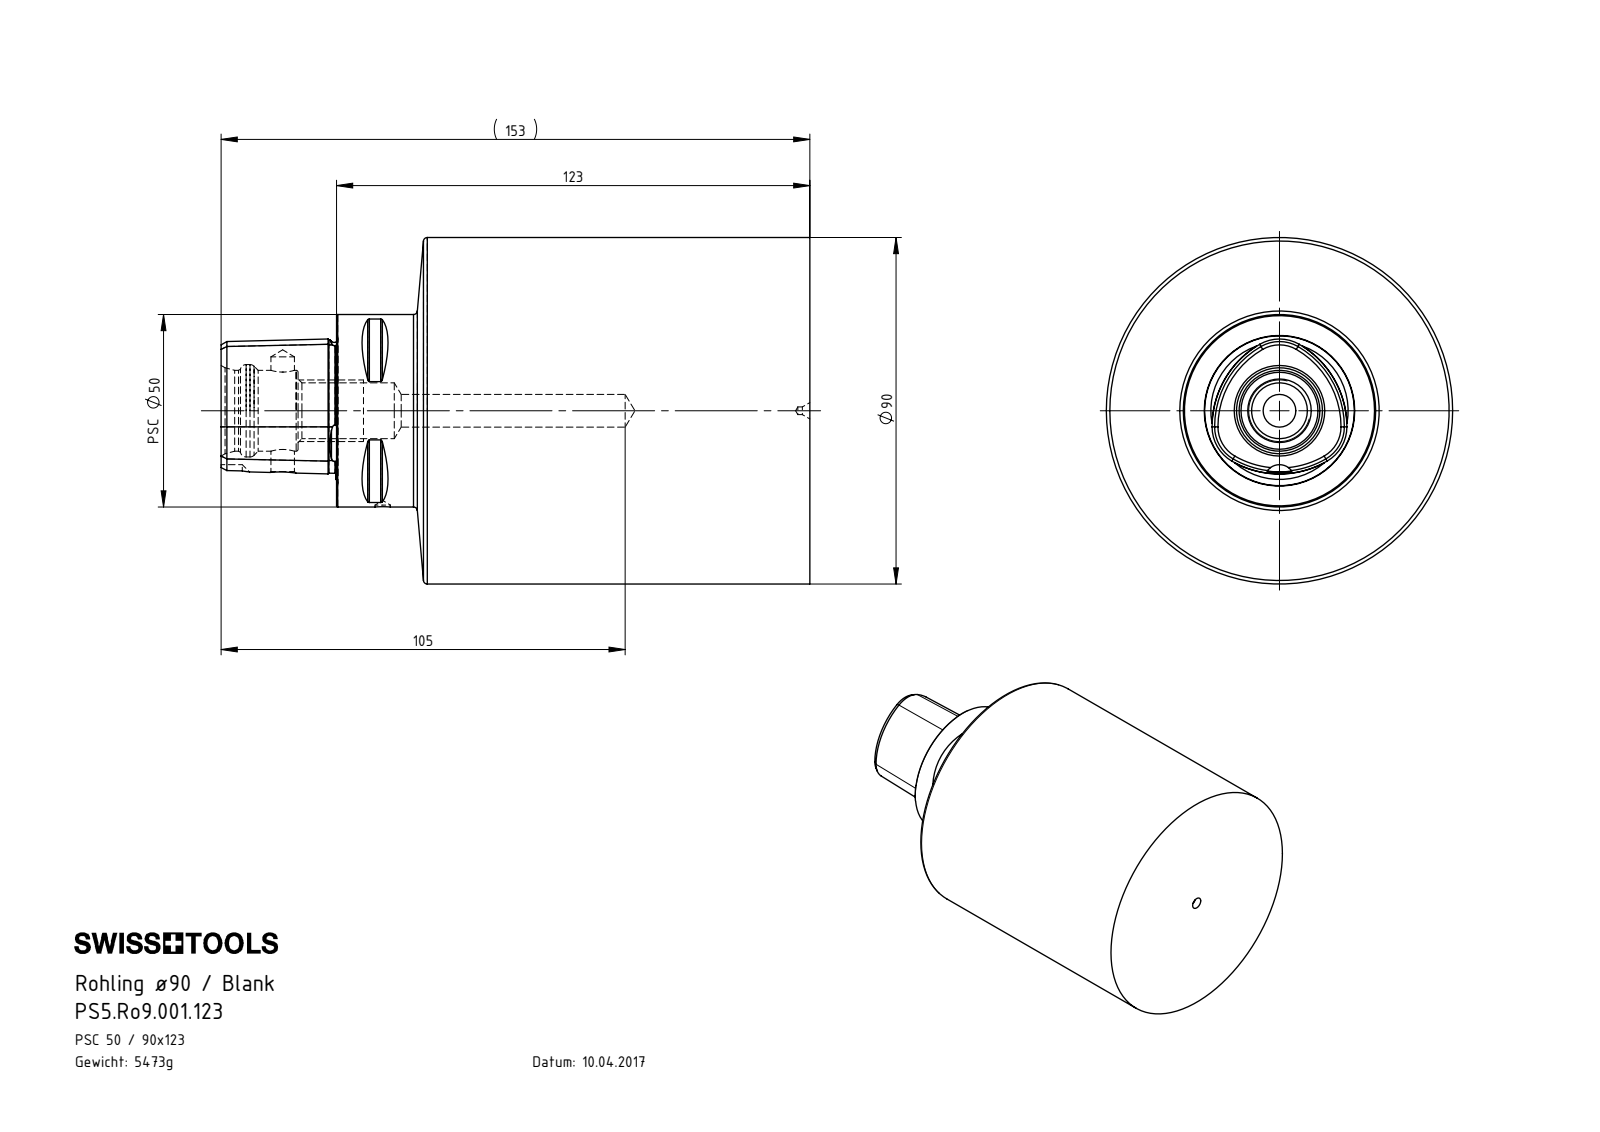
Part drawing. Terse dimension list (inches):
name: PS5.Ro9.001.123
written by: SolidWorks 2017 (AUTOMOTIVE_DESIGN)
unit: in
bodies: 1 solid, 92 faces (19 planar, 20 cylindrical, 53 other)
size: 6.024 × 3.543 × 3.543
volume: 42.54 in³; area: 80.24 in²
holes: 1× ⌀0.079, 1× ⌀0.157, 1× ⌀0.24, 1× ⌀0.335, 1× ⌀0.571, 1× ⌀0.827, 1× ⌀0.945
bosses: 1× ⌀3.543, 1× ⌀1.969
rounds: 8× R0.02, 1× R0.157
face distances: 4.843, 1.181, 6.024, 0.755, 1.748, 0.787, 0.394, 5.236, 1.173, 0.386
hole spacings: 1.024
